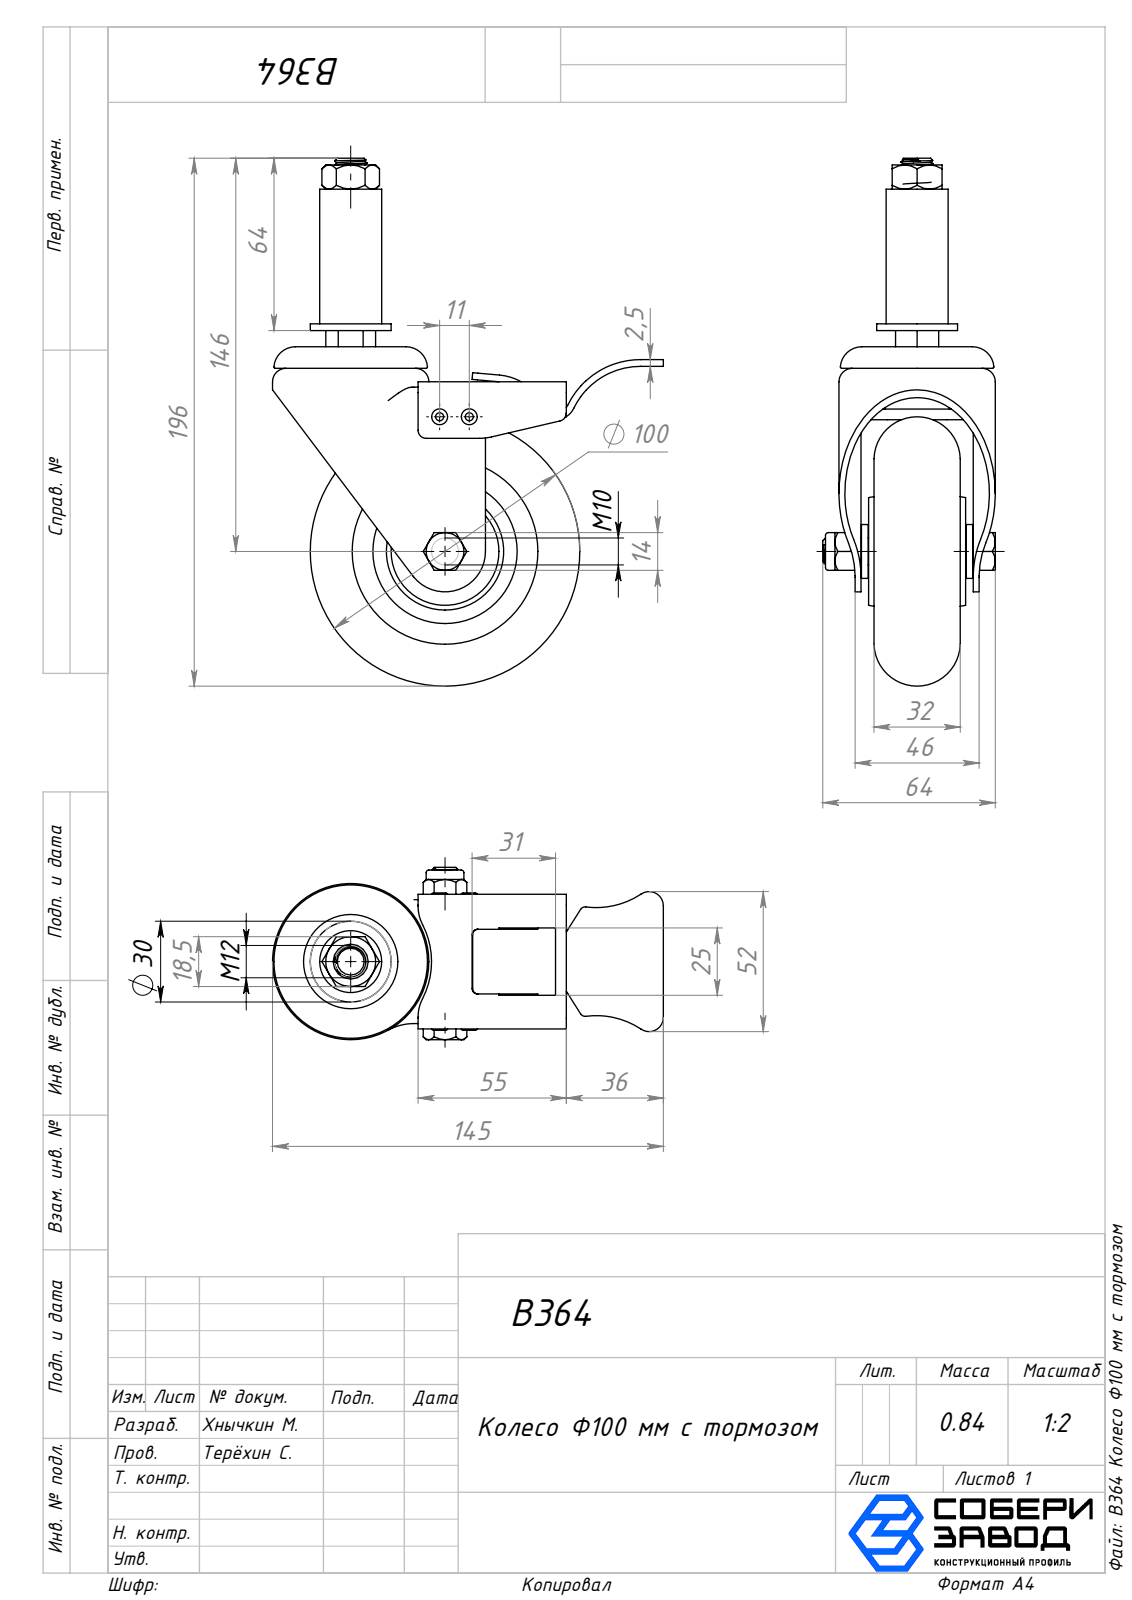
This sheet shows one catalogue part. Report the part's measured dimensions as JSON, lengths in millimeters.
{"part_name": "B364 Колесо Ф100 мм с тормозом", "step_written_by": "SolidWorks 2025 (AUTOMOTIVE_DESIGN)", "units": "millimeters", "bodies": {"solids": 2, "faces": 373, "planar": 102, "cylindrical": 167, "other": 104}, "overall_size": [196, 145, 64], "volume_mm3": 290583, "surface_area_mm2": 79836, "round_holes": [[3, 2], [12.5, 1], [53.64, 1]], "round_bosses_or_shafts": [[58, 1], [41, 1], [30, 1], [23, 1], [20, 1], [18.48, 1], [14, 1], [12, 1]], "partial_cylinders_radius": [[2, 6], [20, 4], [30, 4], [5, 3], [15, 3], [2.82, 2], [3, 2], [4, 2]], "face_to_face_distances": [2.18, 2.82, 7, 43.82, 5, 4.18, 2, 38.82, 41, 10], "hole_center_spacings": [11]}
